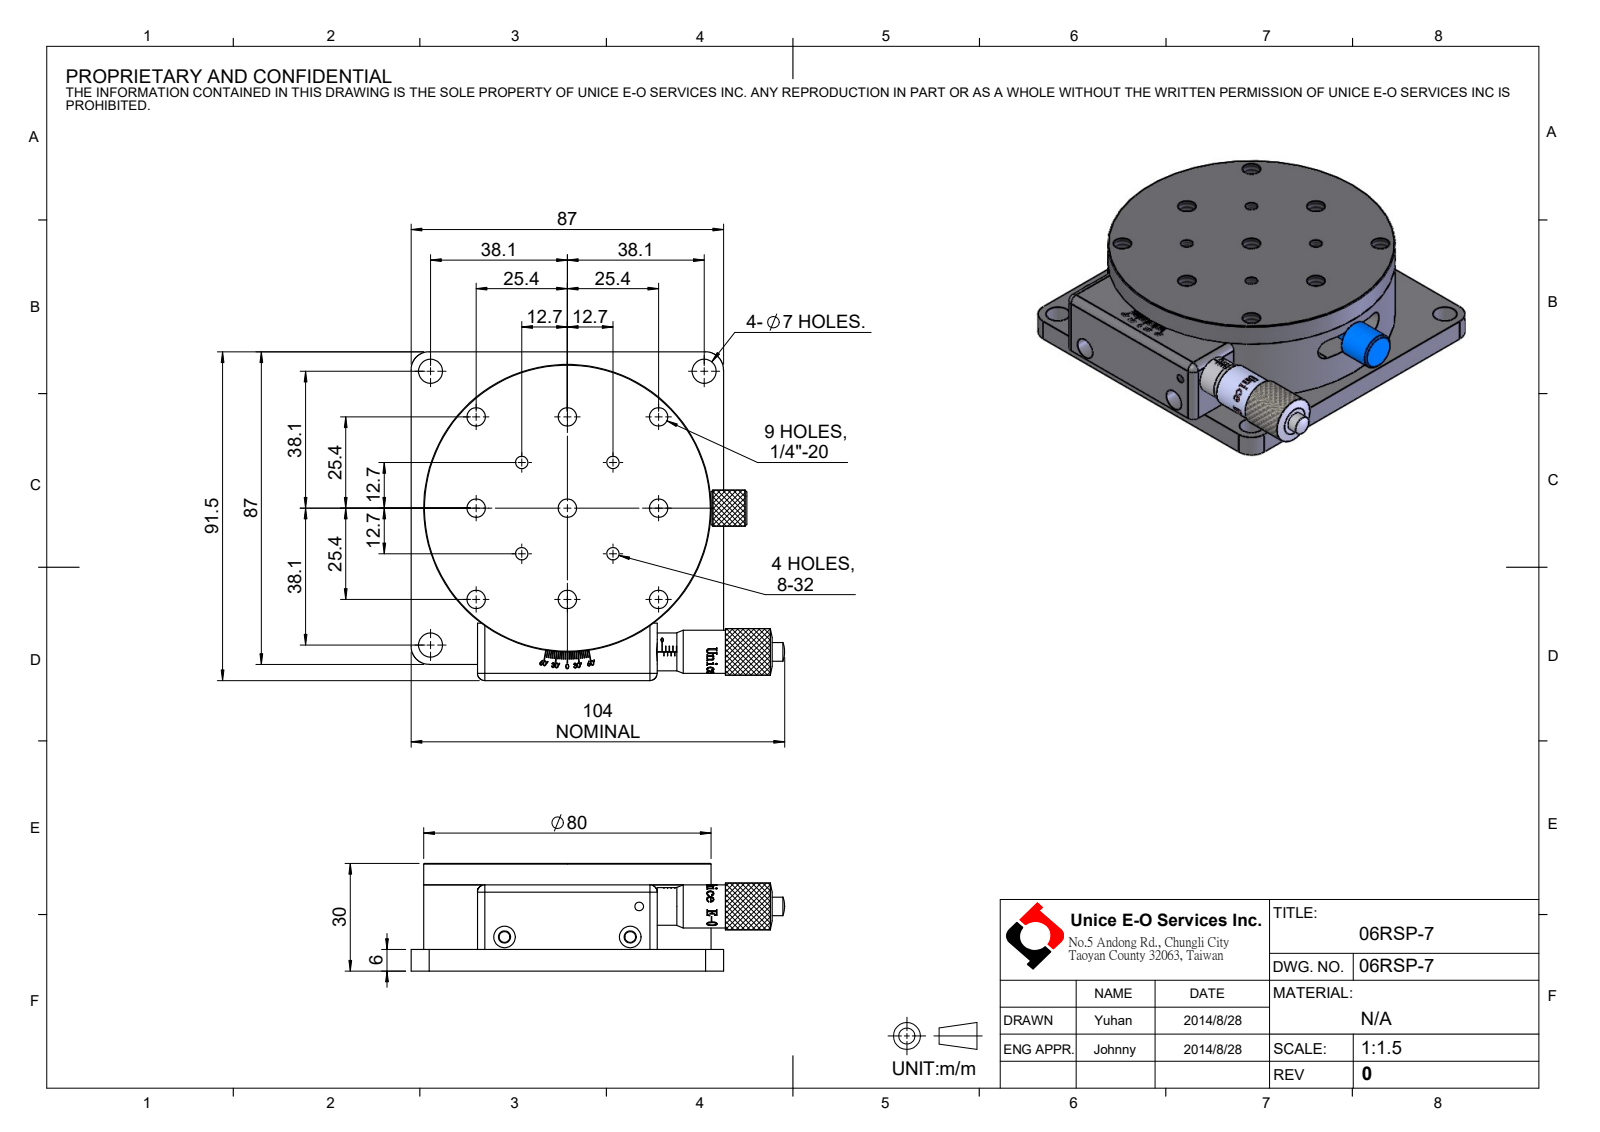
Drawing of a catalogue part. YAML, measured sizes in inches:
part_name: "06RSP-7"
step_written_by: "SolidWorks 2016 (CONFIG_CONTROL_DESIGN)"
units: inches
bodies: {solids: 10, faces: 840, planar: 441, cylindrical: 152, other: 247}
overall_size: [4.094, 3.602, 1.181]
volume: 10.44
surface_area: 94.53
round_holes:
  - {diameter: 0.201, count: 9}
  - {diameter: 0.118, count: 4}
  - {diameter: 0.136, count: 4}
  - {diameter: 0.264, count: 4}
  - {diameter: 0.134, count: 2}
  - {diameter: 0.197, count: 2}
  - {diameter: 0.236, count: 2}
  - {diameter: 0.256, count: 2}
  - {diameter: 0.094, count: 1}
  - {diameter: 0.177, count: 1}
  - {diameter: 0.315, count: 1}
  - {diameter: 0.354, count: 1}
round_bosses_or_shafts:
  - {diameter: 0.394, count: 2}
  - {diameter: 0.157, count: 2}
  - {diameter: 3.15, count: 1}
  - {diameter: 1.732, count: 1}
  - {diameter: 1.26, count: 1}
  - {diameter: 0.512, count: 1}
  - {diameter: 0.472, count: 1}
  - {diameter: 0.413, count: 1}
partial_cylinders:
  - {radius: 0.118, count: 6}
  - {radius: 0.079, count: 5}
  - {radius: 0.197, count: 4}
  - {radius: 0.235, count: 1}
face_to_face_distances: [0.236, 0.945, 0.709, 0.472, 1.181, 0.157, 0.787, 0.079, 0.315, 1.024]
hole_center_spacings: [1.581, 0.707, 1, 2.236, 1.414, 2.121, 2.55, 2.915]
